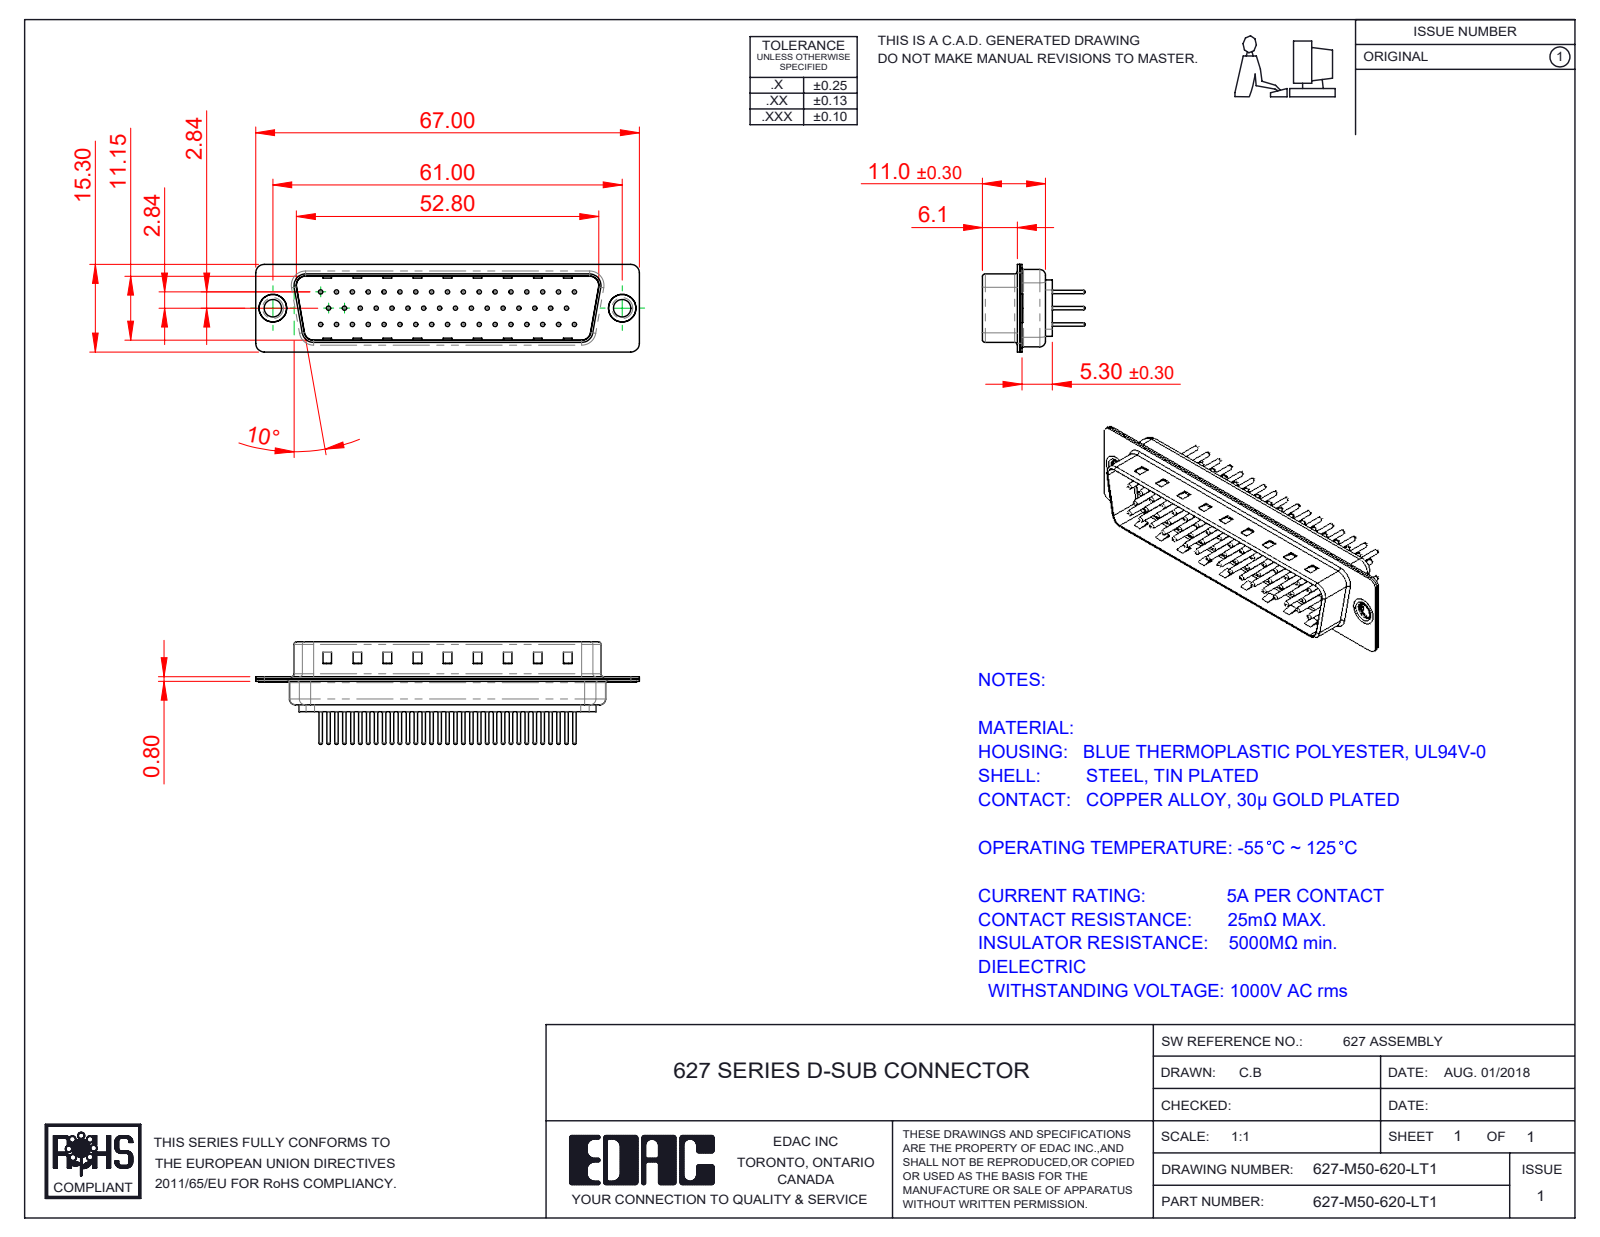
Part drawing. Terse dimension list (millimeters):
name: 627M Shell Rear_50 Contacts; 627M Shell Front_50 Contacts; 627M Contact Row 2_20; 627M Contact Row 1_20 (+4 more)
written by: SolidWorks 2020 (CONFIG_CONTROL_DESIGN)
unit: mm
bodies: 55 solids, 2236 faces (553 planar, 825 cylindrical, 858 other)
size: 67 × 17.9 × 15.3
volume: 4 447 mm³; area: 10 554 mm²
holes: 50× ⌀0.75, 50× ⌀1.6, 50× ⌀2, 2× ⌀3.05, 2× ⌀4, 2× ⌀4.8
bosses: 50× ⌀1.5, 50× ⌀0.6, 2× ⌀5, 2× ⌀4.9, 2× ⌀3.55
rounds: 16× R1.5, 12× R2, 8× R0.5, 8× R1.6, 4× R0.25, 4× R0.6, 4× R0.65, 4× R0.9
face distances: 0.4, 11.55, 5.7, 6.1, 0.78, 0.77, 12.33, 12.32, 13.1, 5.3
hole spacings: 3.16, 2.77, 5.54, 8.31, 11.08, 13.85, 16.62, 5.03
